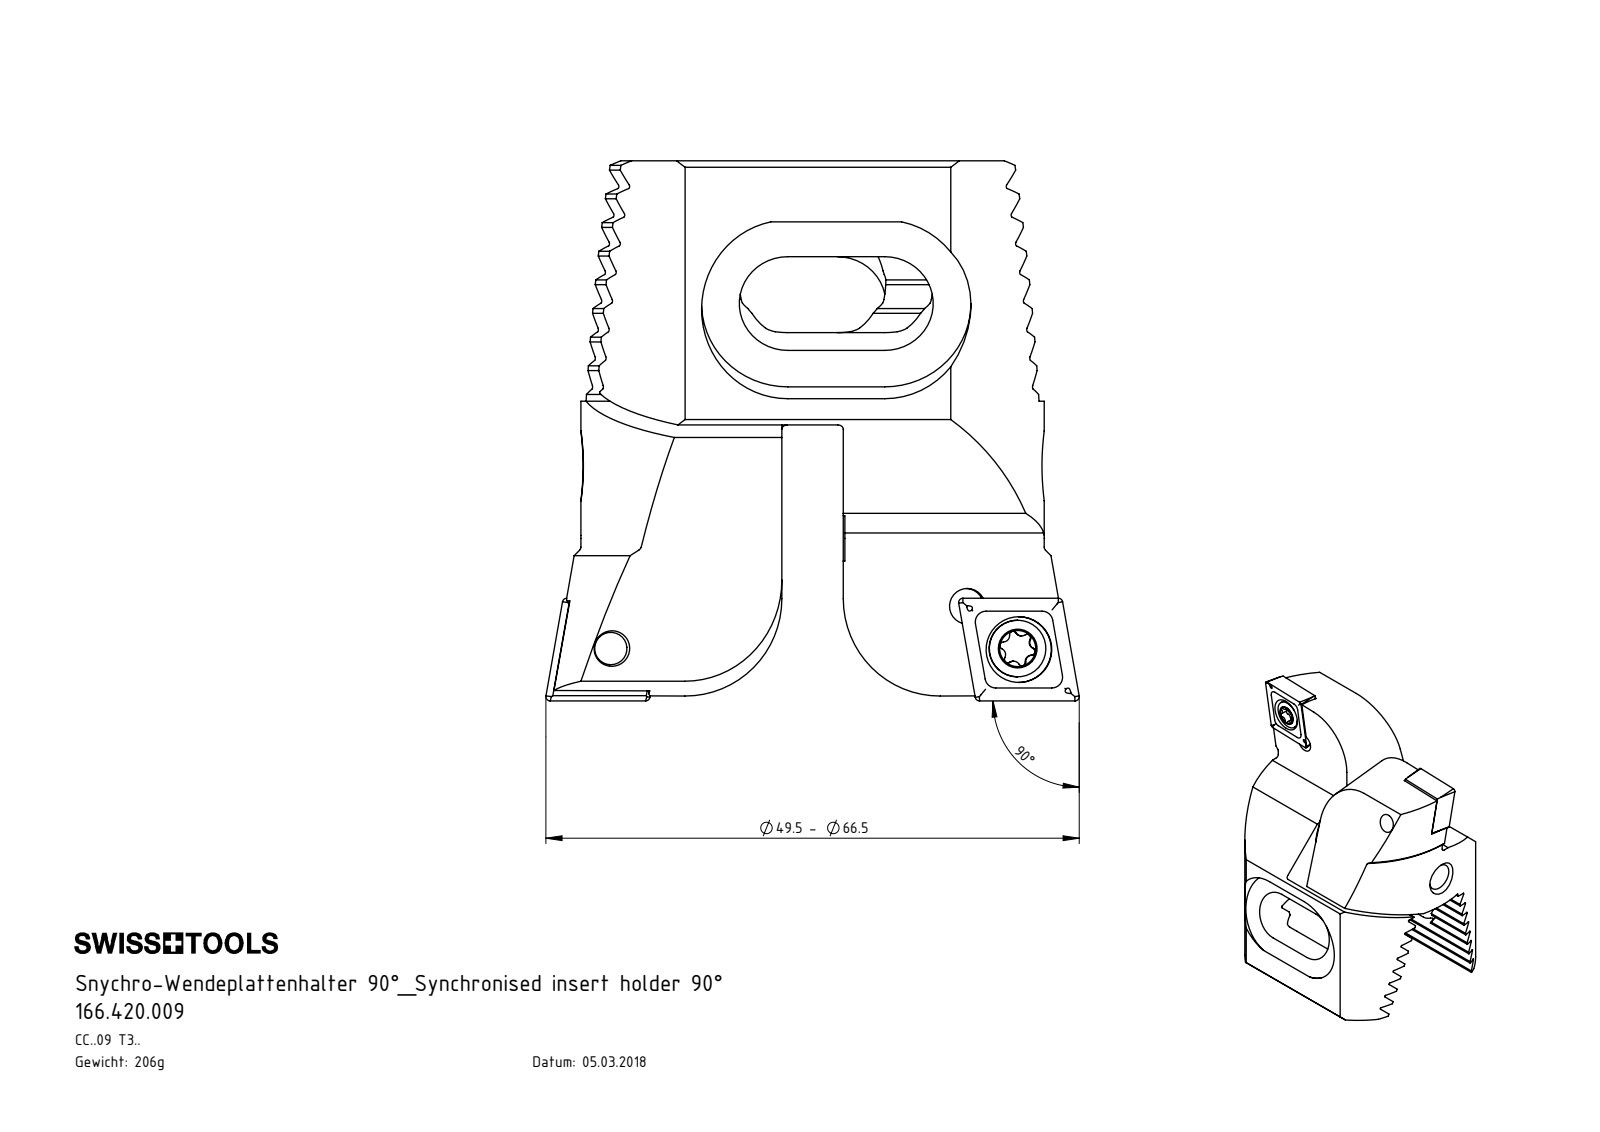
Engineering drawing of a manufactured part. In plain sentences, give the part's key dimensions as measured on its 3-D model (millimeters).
The part is named "Z42-ER3.000.040; 166.420.009; Z42-WCB.001.028_A; Z42-ER3.002.005_A (+4 more)". Its 3-D file was written by "SolidWorks 2017 (CONFIG_CONTROL_DESIGN)". It is 11 solids with 525 faces: 205 planar, 170 cylindrical and 150 other. Overall it measures 50.1 by 49.5 by 34.2 millimeters. Its volume is 27 942 cubic millimeters and its surface area 14 559 square millimeters. Round holes: 7 of diameter 3.3, 2 of diameter 1, 2 of diameter 4.4, 2 of diameter 6.1, 1 of diameter 5. Round bosses or shafts: 3 of diameter 3, 2 of diameter 5.25, 2 of diameter 4, 1 of diameter 17, 1 of diameter 6, 1 of diameter 3.8. Partial cylindrical surfaces (rounded edges, fillets, slot ends): 16 of radius 0.2, 12 of radius 0.34, 12 of radius 0.59, 8 of radius 1, 4 of radius 0.5, 4 of radius 4.5, 4 of radius 8, 2 of radius 9. The main face-to-face distances are 2.38, 4.76, 11.91, 9.53, 14.29, 7.15, 4.99, 7.14, 1.04, 16.67. The hole center spacings are 6.1, 13, 33.59, 6.25, 6.26, 25.12, 28.69, 33.71.
